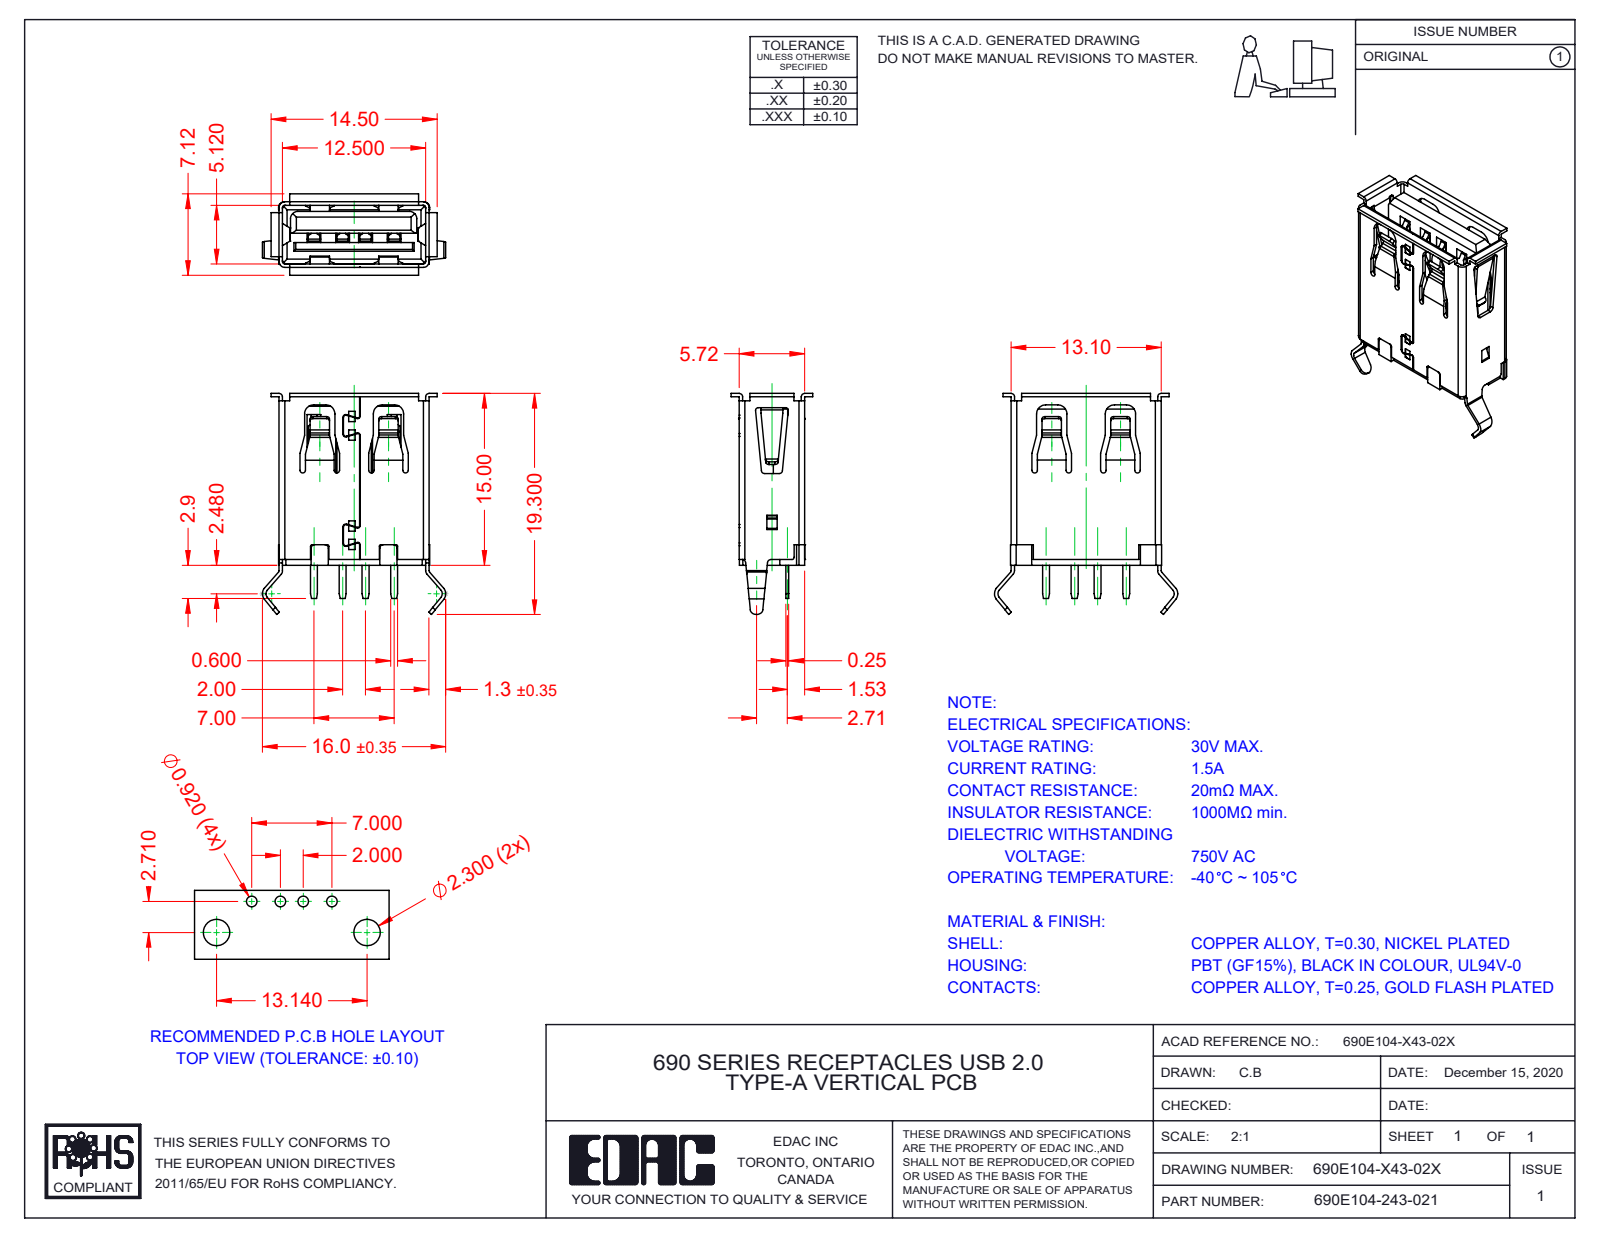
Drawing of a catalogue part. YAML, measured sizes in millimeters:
part_name: "690E104-243-021; Shell 690-104EX43-02X; Contact 690E104-X43-02X; Insulator2 690E104-X43-02X_Black (+1 more)"
step_written_by: "SolidWorks 2020 (AUTOMOTIVE_DESIGN)"
units: millimeters
bodies: {solids: 7, faces: 825, planar: 618, cylindrical: 207, other: 0}
overall_size: [19.3, 16, 7.12]
volume: 620
surface_area: 2264
partial_cylinders:
  - {radius: 0.2, count: 37}
  - {radius: 0.3, count: 26}
  - {radius: 0.15, count: 25}
  - {radius: 0.5, count: 15}
  - {radius: 0.25, count: 13}
  - {radius: 0.8, count: 6}
  - {radius: 0.56, count: 4}
  - {radius: 0.62, count: 4}
face_to_face_distances: [5.42, 5.12, 5.72, 2.5, 1.09, 12.8, 1.2, 4.5, 1.39, 4.03]
